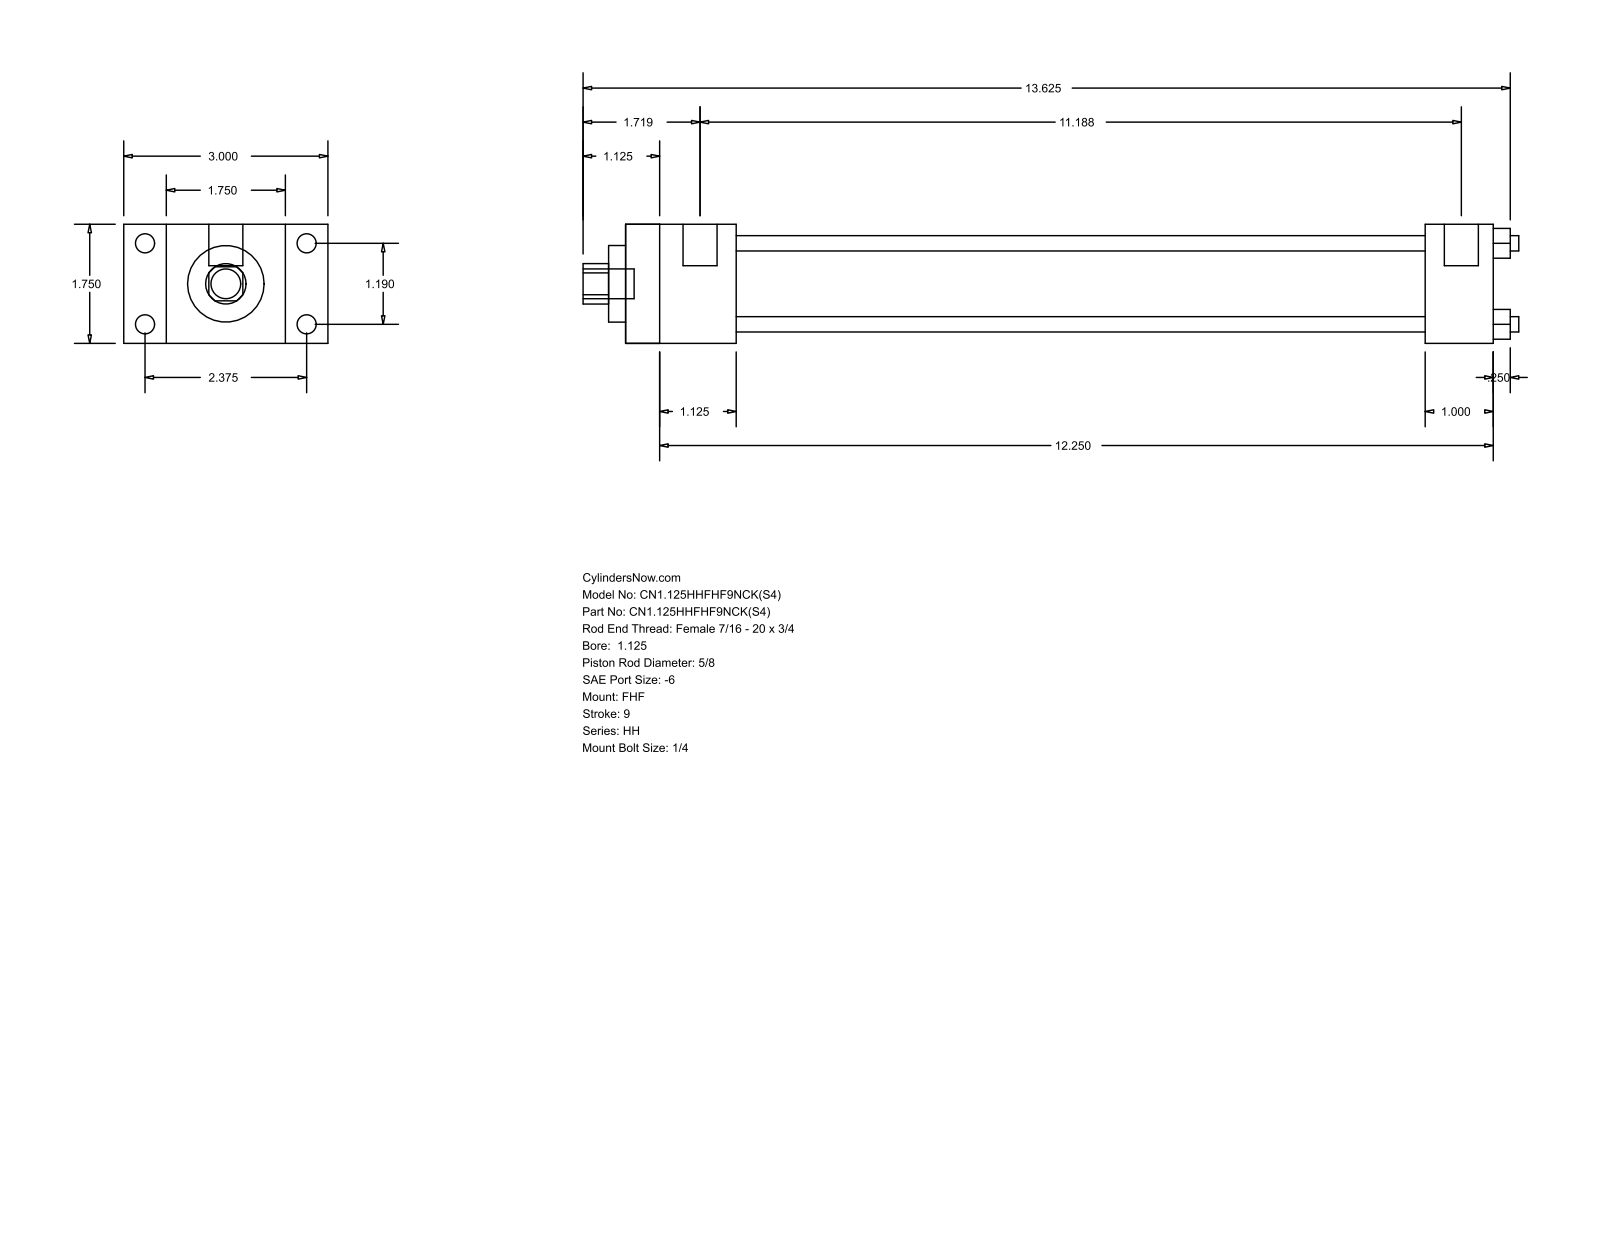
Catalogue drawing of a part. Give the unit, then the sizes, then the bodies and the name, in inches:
Units: inches
Overall size (bounding box): 13.75 × 3 × 1.75
Round holes (diameter × count): ⌀0.225 ×4, ⌀0.625 ×1, ⌀1.125 ×1, ⌀1.375 ×1
Round bosses / shafts (diameter × count): ⌀0.281 ×4, ⌀0.219 ×4, ⌀0.5 ×2, ⌀0.437 ×1
Partial cylindrical surfaces — rounded edges, fillets, slot ends (radius × count): R0.297 ×1
Main face-to-face distances: 1.75, 0.625, 2.375, 1.625, 3, 12.75, 11.125, 11.75, 10.125, 1
Hole centre spacings: 0.841, 1.19, 1.683
Bodies: 0 solids, 88 faces (60 planar, 28 cylindrical, 0 other)
Part name (STEP PRODUCT): HH_FHF__0112_0.625
STEP written by: GSSL Pune (CONFIG_CONTROL_DESIGN)
